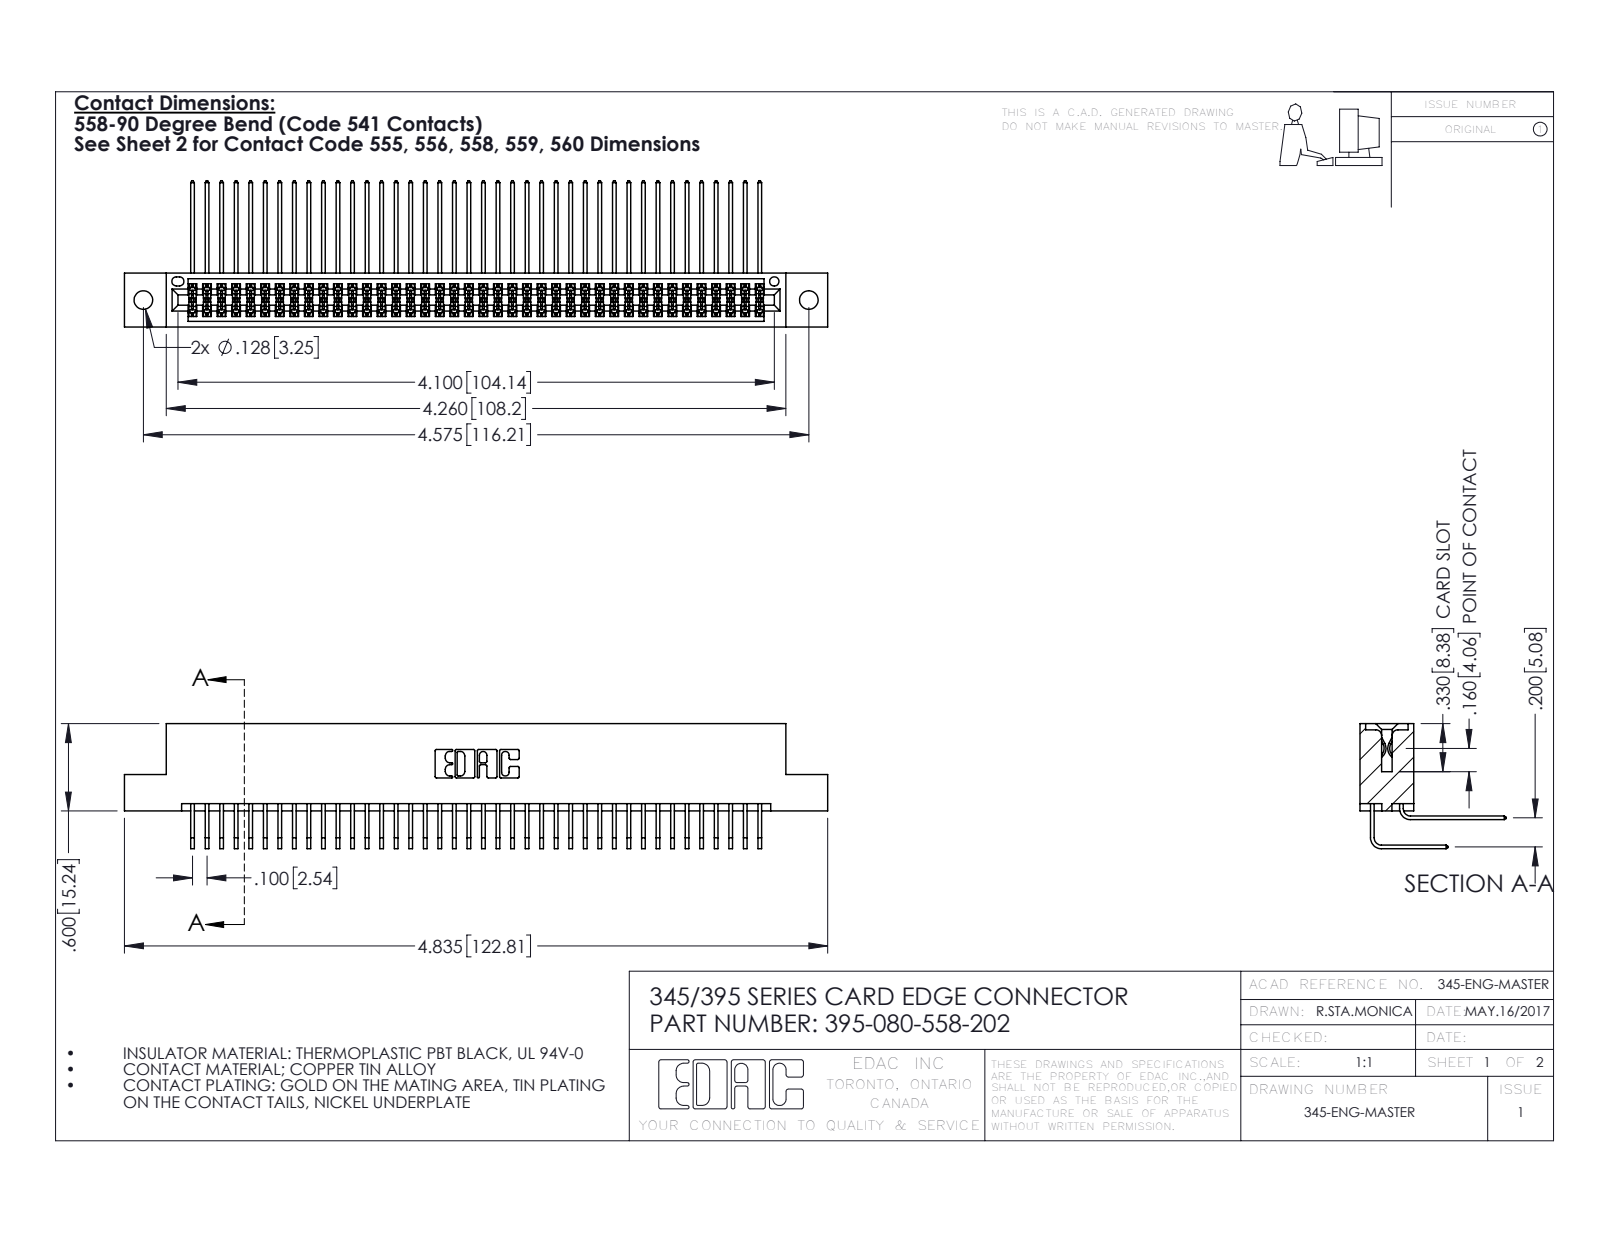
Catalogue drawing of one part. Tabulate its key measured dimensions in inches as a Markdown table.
| quantity | value |
| --- | --- |
| part name | 345 Part_Flush Mounting Lugs - 0.128 Dia; 395-080-558-202; 345-292-001_558 Tail - 2; 345-292-001_558 559 Tail - 1 |
| STEP written by | SolidWorks 2016 (CONFIG_CONTROL_DESIGN) |
| units | inches |
| bodies | 81 solids, 4286 faces (2880 planar, 1406 cylindrical, 0 other) |
| overall size | 4.835 × 1.005 × 0.859 |
| volume | 0.753 in³ |
| surface area | 31.14 in² |
| round holes (diameter × count) | 0.128 × 2, 0.064 × 1 |
| partial cylindrical surfaces (radius × count) | 0.006 × 121, 0.01 × 22, 0.007 × 6, 0.031 × 6, 0.026 × 3, 0.014 × 2, 0.019 × 2, 0.022 × 2 |
| main face-to-face distances | 0.072, 0.298, 0.2, 0.37, 0.098, 0.272, 0.025, 0.225, 0.025, 0.175 |
| hole center spacings | 0.27, 4.339, 4.575 |
